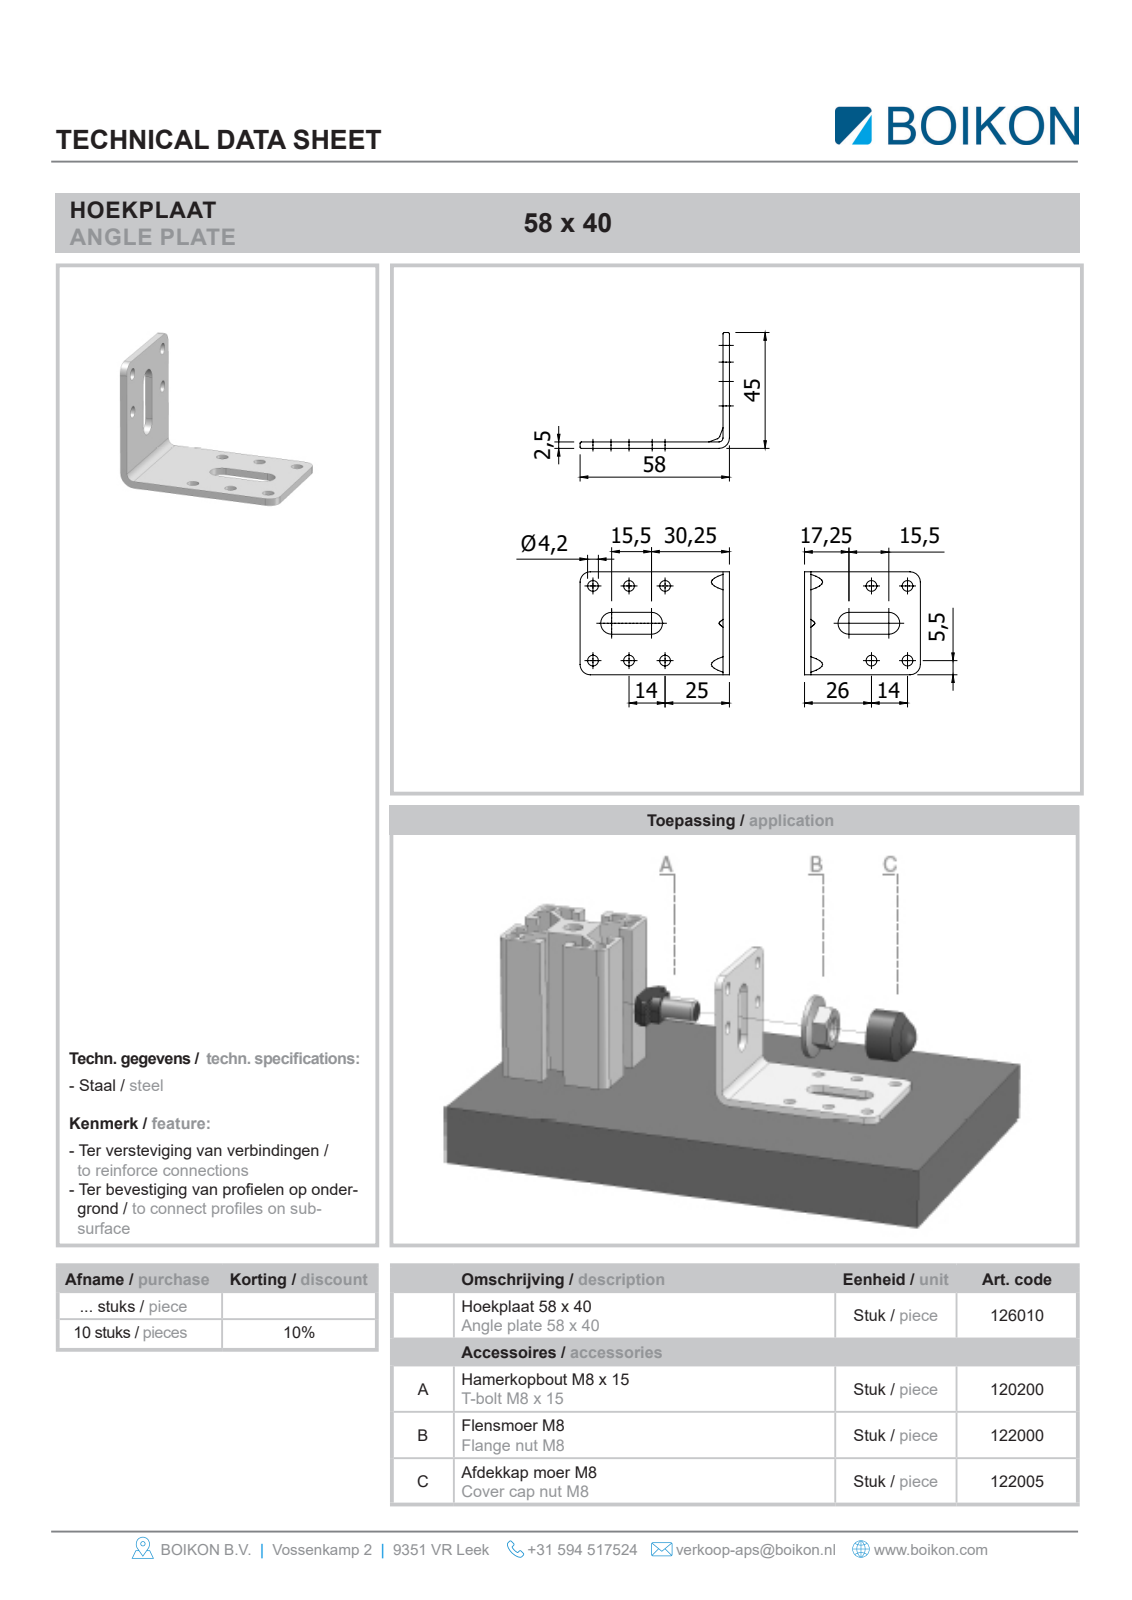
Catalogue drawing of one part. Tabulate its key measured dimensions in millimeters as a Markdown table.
| quantity | value |
| --- | --- |
| part name | Root; 126010 Hoekplaat 58 x 40BOIKON; 122000Flensmoer M8BOIKON; 122005Afdekkap voor moer M8BOIKON (+1 more) |
| STEP written by | HiCAD 2013 1802.4 Build 509 (AUTOMOTIVE_DESIGN) |
| units | millimeters |
| bodies | 7 solids, 224 faces (150 planar, 48 cylindrical, 26 other) |
| overall size | 68.2 × 55.2 × 40 |
| volume | 17 701 mm³ |
| surface area | 14 696 mm² |
| round holes (diameter × count) | 4.2 × 10, 8 × 2 |
| round bosses / shafts (diameter × count) | 21 × 2, 16.8 × 2, 6.47 × 2 |
| partial cylindrical surfaces (radius × count) | 1 × 8, 0.4 × 4, 4 × 4, 4.25 × 4, 5 × 3, 9.7 × 2, 2.5 × 1 |
| main face-to-face distances | 2.5, 24.25, 15.75, 13, 40, 9.5, 7, 8.5, 13.5, 26.5 |
| hole center spacings | 14, 32.2, 29, 14.53, 20.86, 19.47, 28, 40.31 |
